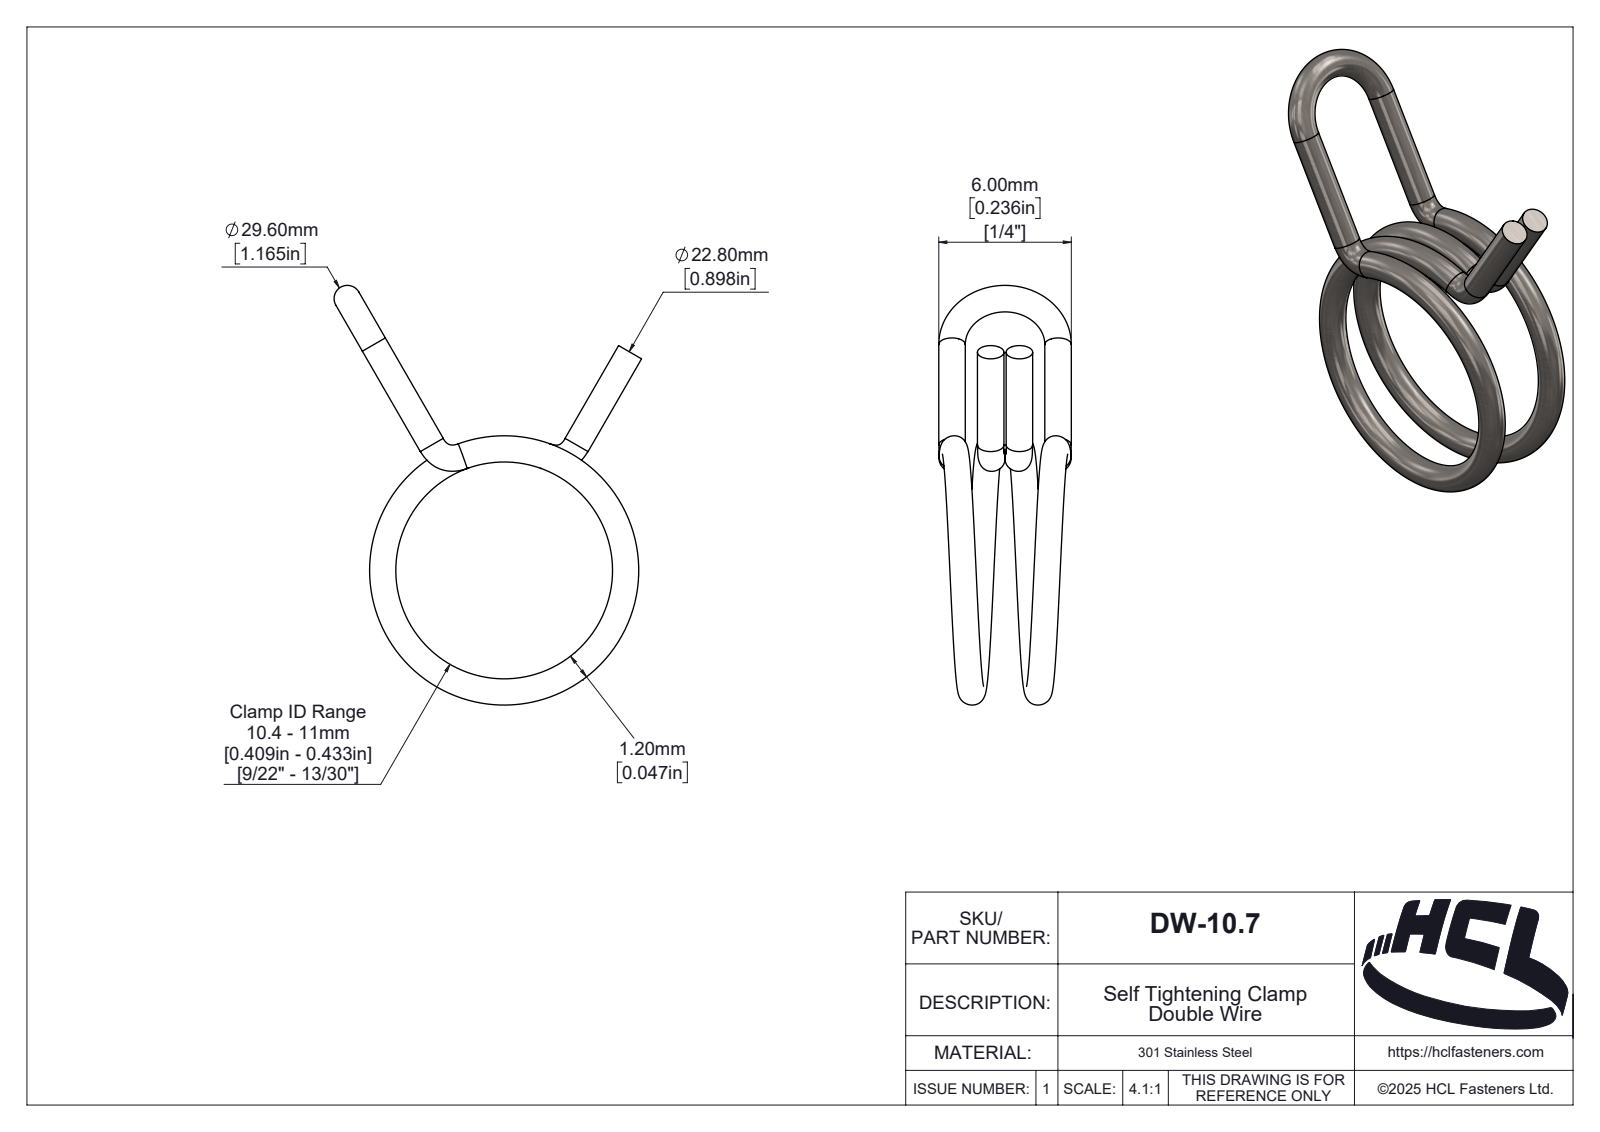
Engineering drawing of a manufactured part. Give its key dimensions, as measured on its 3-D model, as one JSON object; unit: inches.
{"part_name": "DW-10.7", "step_written_by": "SolidWorks 2025 (AUTOMOTIVE_DESIGN)", "units": "inches", "bodies": {"solids": 1, "faces": 132, "planar": 14, "cylindrical": 53, "other": 65}, "overall_size": [0.748, 0.548, 0.236], "volume_in3": 0.008, "surface_area_in2": 0.649, "round_bosses_or_shafts": [[0.047, 4]], "partial_cylinders_radius": [[0.006, 1], [0.008, 1], [0.008, 1], [0.01, 1], [0.014, 1], [0.019, 1], [0.024, 1], [0.027, 1]]}
